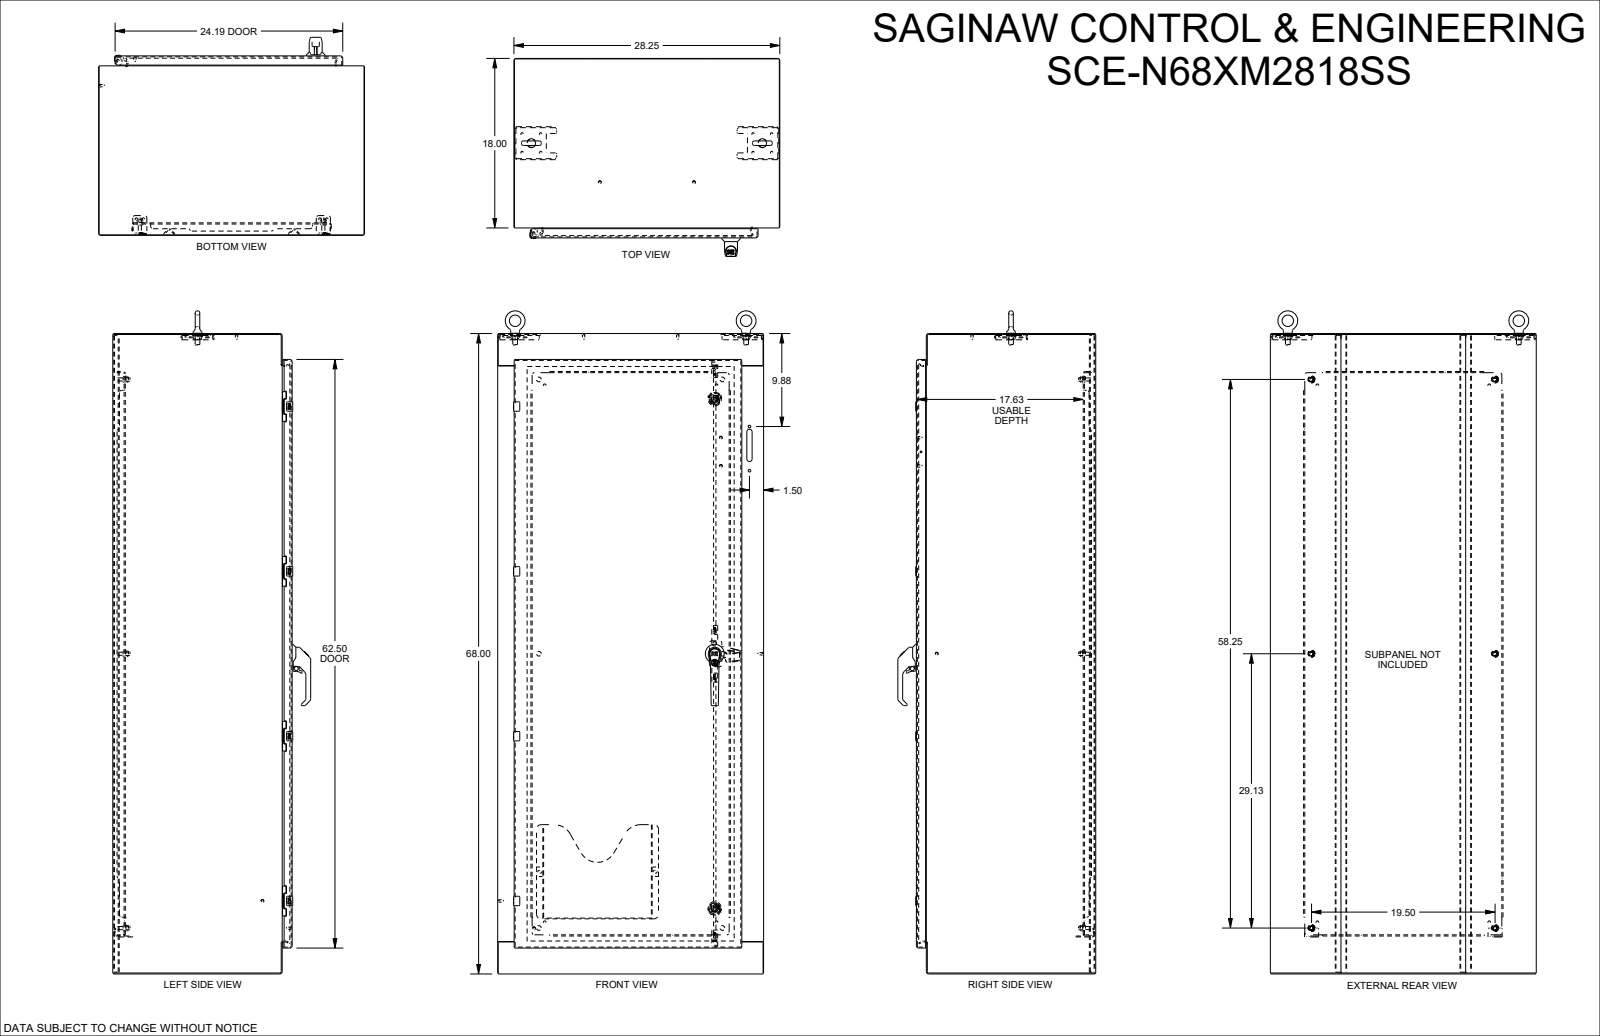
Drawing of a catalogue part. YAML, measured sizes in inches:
part_name: "SCE-N68XM2818"
step_written_by: "SolidWorks 2023 (AUTOMOTIVE_DESIGN)"
units: inches
bodies: {solids: 22, faces: 3140, planar: 1331, cylindrical: 1021, other: 788}
overall_size: [70.945, 28.25, 21.046]
volume: 851.6
surface_area: 16255
round_holes:
  - {diameter: 0.25, count: 10}
  - {diameter: 0.205, count: 8}
  - {diameter: 0.244, count: 8}
  - {diameter: 0.375, count: 8}
  - {diameter: 0.04, count: 4}
  - {diameter: 0.17, count: 4}
  - {diameter: 0.218, count: 4}
  - {diameter: 0.256, count: 4}
  - {diameter: 0.281, count: 2}
  - {diameter: 0.343, count: 2}
  - {diameter: 0.36, count: 2}
  - {diameter: 0.875, count: 2}
round_bosses_or_shafts:
  - {diameter: 0.17, count: 12}
  - {diameter: 0.25, count: 8}
  - {diameter: 0.24, count: 8}
  - {diameter: 0.196, count: 5}
  - {diameter: 1.4, count: 2}
  - {diameter: 1.173, count: 2}
  - {diameter: 0.6, count: 2}
  - {diameter: 0.341, count: 2}
partial_cylinders:
  - {radius: 0.03, count: 96}
  - {radius: 0.015, count: 68}
  - {radius: 0.04, count: 37}
  - {radius: 0.062, count: 32}
  - {radius: 0.125, count: 31}
  - {radius: 0.02, count: 24}
  - {radius: 0.039, count: 22}
  - {radius: 0.079, count: 21}
face_to_face_distances: [0.104, 18.954, 28.146, 18.85, 19.058, 28.25, 28.042, 17.896, 1.058, 67.896]
hole_center_spacings: [17.5, 35, 0.493, 0.494, 0.984, 1.399, 1.4, 1.979]
